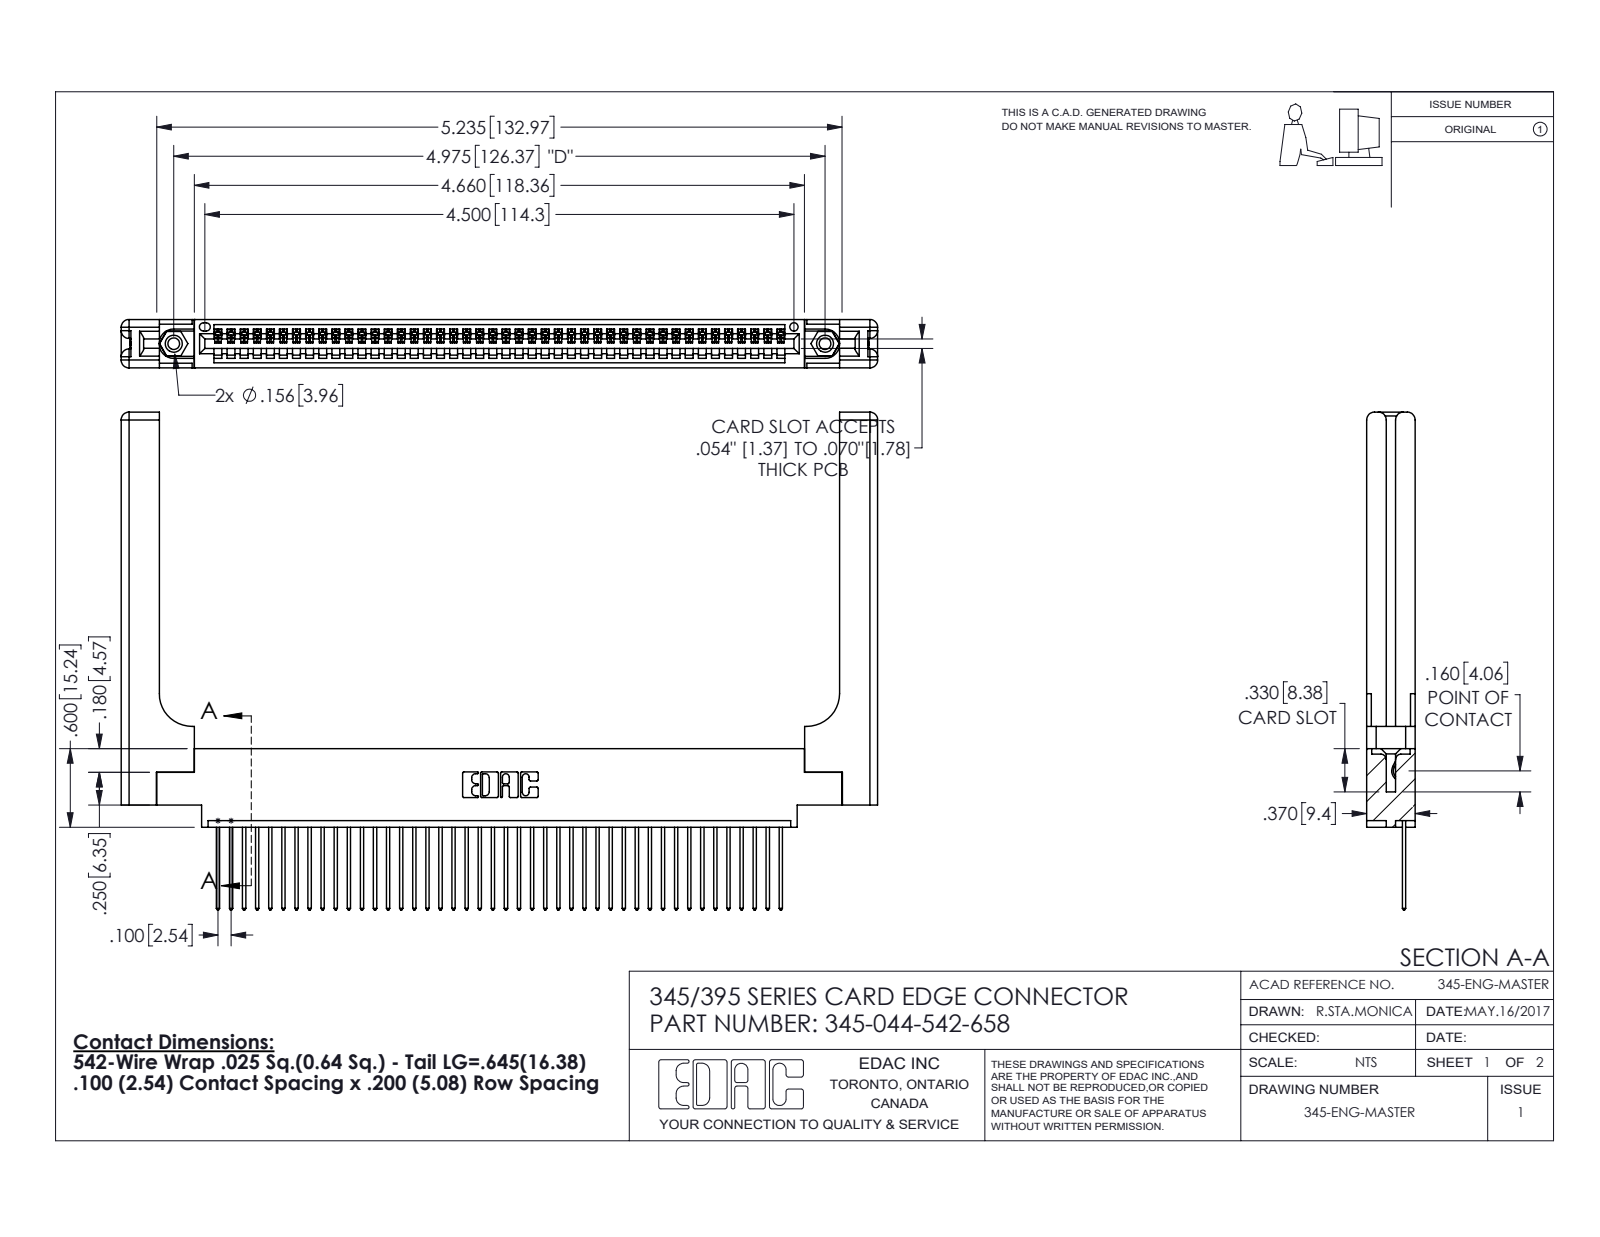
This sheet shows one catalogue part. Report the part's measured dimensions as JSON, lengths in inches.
{"part_name": "345 Part_0.170 Offset - 0.156 Dia-TH; 345-220-058_345-220-058; 345-292-001_345-293-142; 345-250-001_345-250-001-102 (+1 more)", "step_written_by": "SolidWorks 2016 (CONFIG_CONTROL_DESIGN)", "units": "inches", "bodies": {"solids": 49, "faces": 2938, "planar": 1992, "cylindrical": 886, "other": 60}, "overall_size": [5.779, 3.802, 0.37], "volume_in3": 1.37, "surface_area_in2": 38.14, "round_holes": [[0.089, 2], [0.125, 2], [0.156, 2], [0.064, 1]], "round_bosses_or_shafts": [[0.155, 2]], "partial_cylinders_radius": [[0.006, 88], [0.01, 88], [0.01, 22], [0.06, 16], [0.007, 6], [0.031, 6], [0.026, 3], [0.03, 2]], "face_to_face_distances": [0.072, 0.37, 0.298, 0.098, 0.272, 0.025, 0.2, 0.225, 0.148, 0.15], "hole_center_spacings": [0.27, 4.739, 4.975]}
